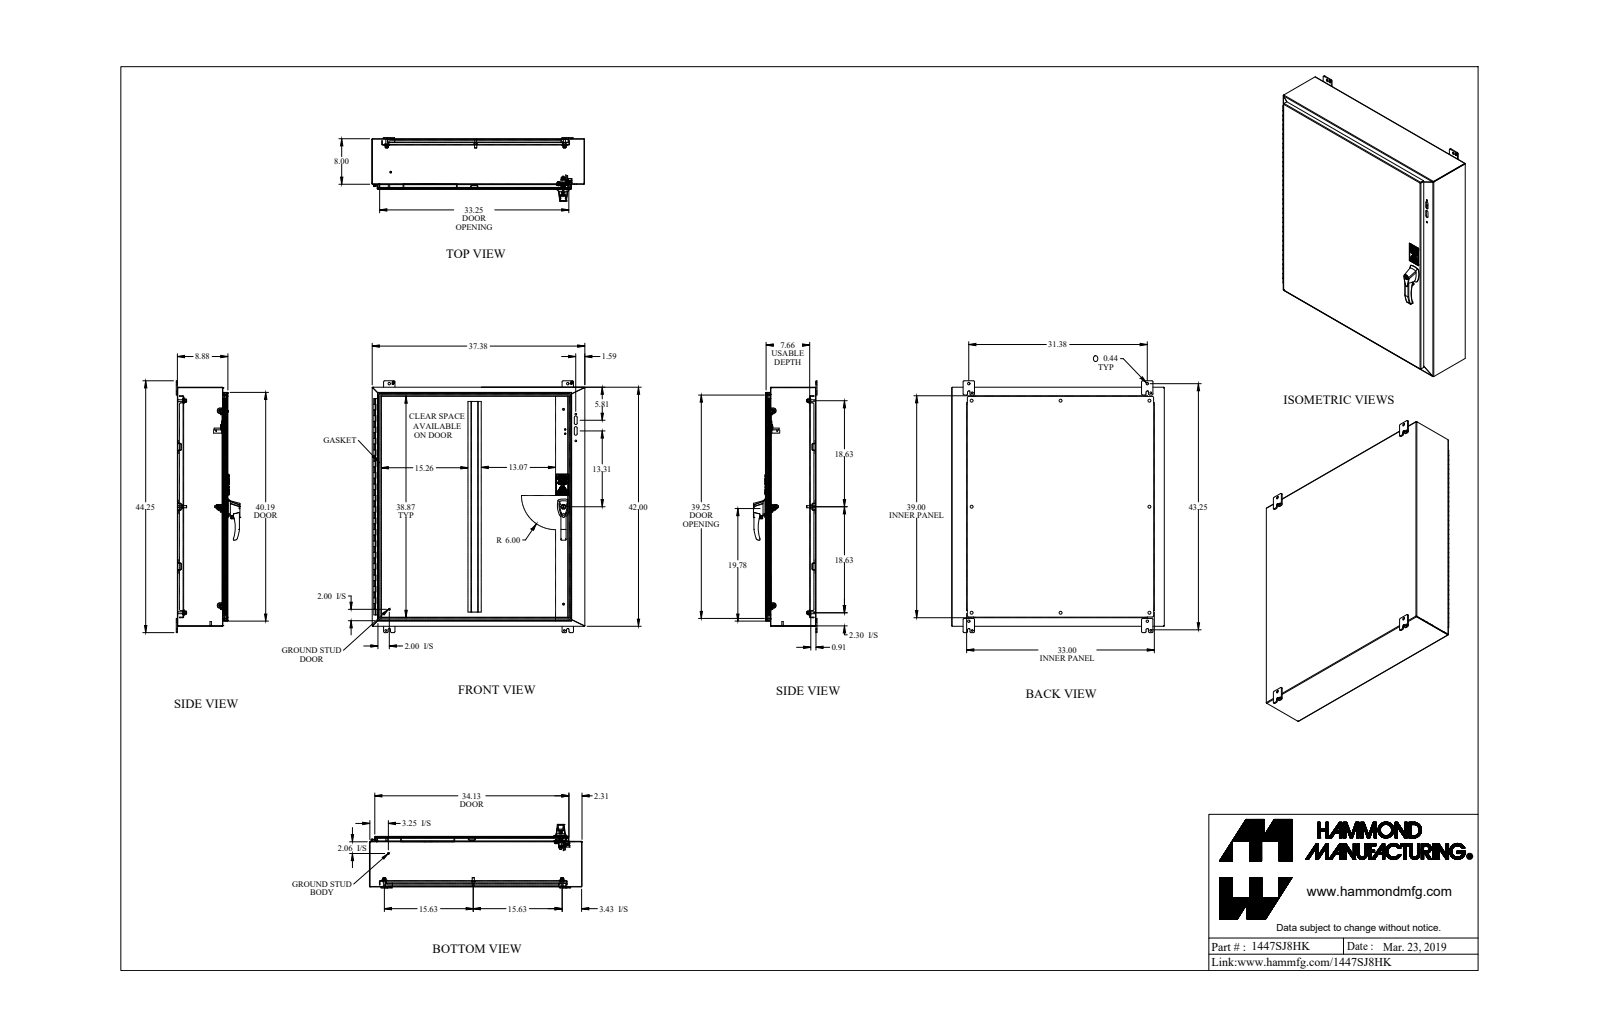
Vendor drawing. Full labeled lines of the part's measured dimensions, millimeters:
Part name (STEP PRODUCT): 1447SJ8HK
STEP written by: SolidWorks 2019 (AUTOMOTIVE_DESIGN)
Units: millimetres
Bodies: 69 solids, 1579 faces (971 planar, 468 cylindrical, 140 other)
Overall size (bounding box): 1123.94 × 949.33 × 283.9
Volume: 8 835 000 mm³ · Surface area: 8 851 000 mm²
Round holes (diameter × count): ⌀12.7 ×8, ⌀4.47 ×6, ⌀7.94 ×6, ⌀7.81 ×4, ⌀11.11 ×4, ⌀11.3 ×4, ⌀6.35 ×3, ⌀6.73 ×3, ⌀10.49 ×3, ⌀3.97 ×2, ⌀4.39 ×2, ⌀4.98 ×2
Round bosses / shafts (diameter × count): ⌀9.53 ×13, ⌀6.35 ×9, ⌀16.51 ×8, ⌀8.38 ×8, ⌀25.4 ×7, ⌀3.97 ×6, ⌀16 ×2, ⌀12.95 ×2
Partial cylindrical surfaces — rounded edges, fillets, slot ends (radius × count): R4.76 ×38, R2 ×28, R6.35 ×21, R0.17 ×16, R2.93 ×16, R3.17 ×16, R0.76 ×10, R3.83 ×8
Main face-to-face distances: 1.83, 223.6, 221.77, 225.43, 2.41, 197.39, 195.56, 26.21, 28.04, 199.8
Hole centre spacings: 796.93, 28.21, 617.5, 766.9, 793.75, 946.15, 44.08, 44.09
